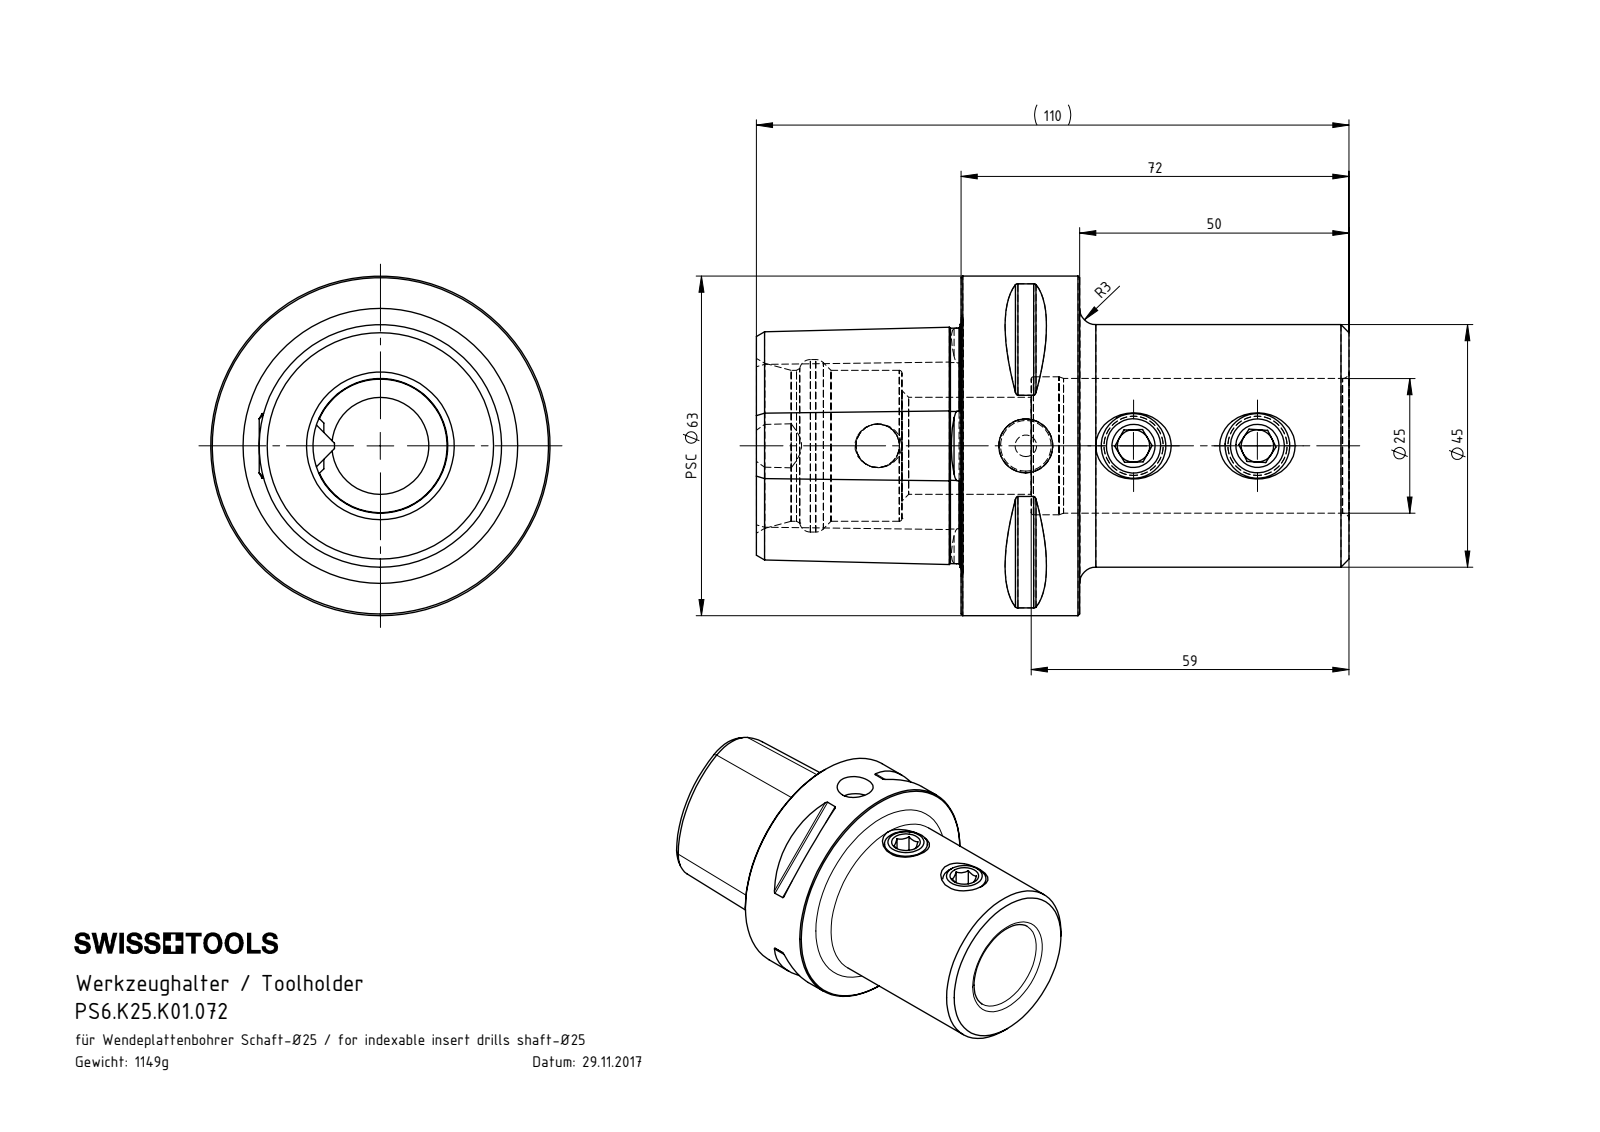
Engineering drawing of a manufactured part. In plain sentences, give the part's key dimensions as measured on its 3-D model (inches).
The part is named "PS6-K25.K01.072_C; K32-ER2.012.014; K32-ER1.012.012_M12x12; PS6.K25.K01.072". Its 3-D file was written by "SolidWorks 2017 (AUTOMOTIVE_DESIGN)". It is 3 solids with 200 faces: 50 planar, 43 cylindrical and 107 other. Overall it measures 4.331 by 2.48 by 2.48 inches. Its volume is 8.962 cubic inches and its surface area 50.52 square inches. Round holes: 2 of diameter 0.236, 2 of diameter 0.433, 1 of diameter 0.319, 1 of diameter 0.394, 1 of diameter 0.709, 1 of diameter 0.984, 1 of diameter 1.008, 1 of diameter 1.102, 1 of diameter 1.26. Round bosses or shafts: 2 of diameter 0.472, 1 of diameter 2.48, 1 of diameter 1.772. Partial cylindrical surfaces (rounded edges, fillets, slot ends): 8 of radius 0.02, 1 of radius 0.236. The main face-to-face distances are 0.866, 2.835, 1.969, 1.496, 2.362, 4.331, 0.98, 1.063, 0.433, 1.299. The hole center spacings are 0.787, 0.906, 1.083, 1.693, 1.87, 2.776.
